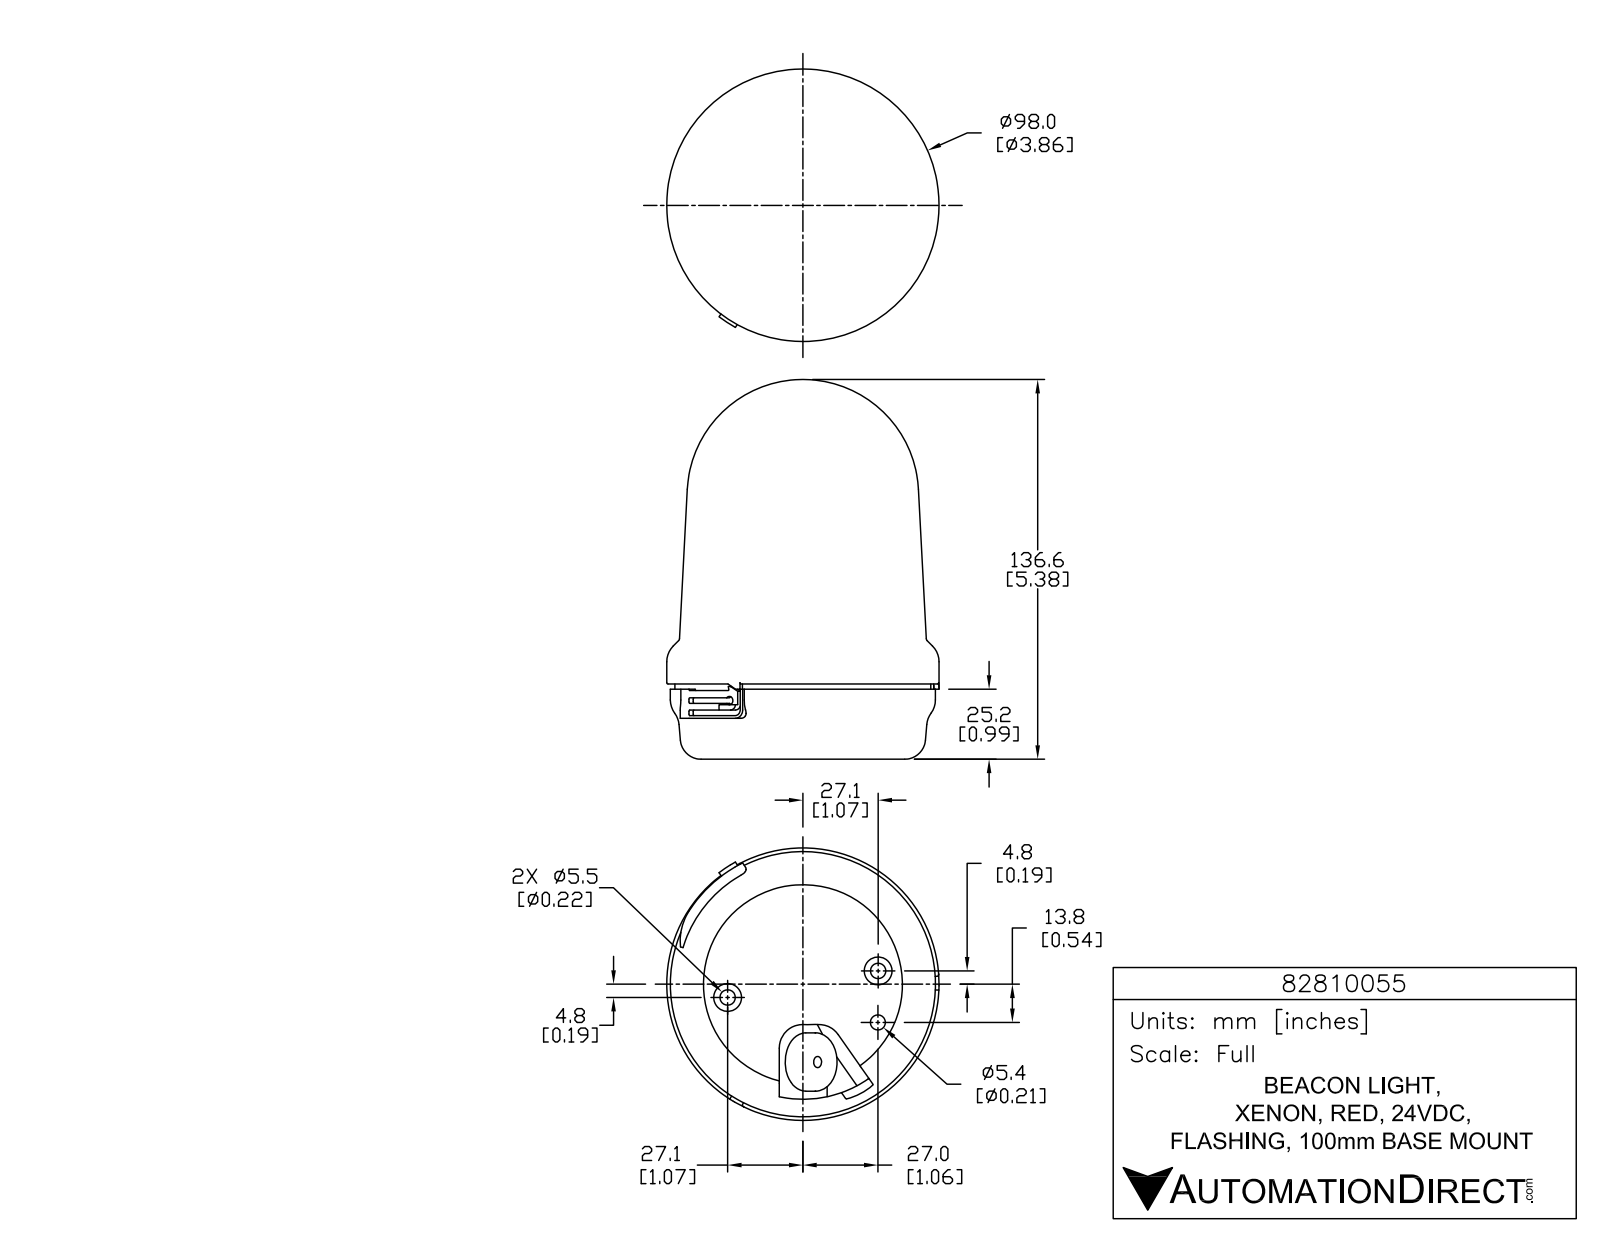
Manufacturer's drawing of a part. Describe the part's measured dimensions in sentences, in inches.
The part is named "82810055". Its 3-D file was written by "SolidWorks 2015 (AUTOMOTIVE_DESIGN)". It is 1 solid with 872 faces: 566 planar, 204 cylindrical and 102 other. Overall it measures 5.378 by 3.858 by 3.858 inches. Its volume is 44.69 cubic inches and its surface area 73.66 square inches. Round holes: 3 of diameter 0.059, 2 of diameter 0.217, 1 of diameter 0.157, 1 of diameter 0.213, 1 of diameter 2.819. Round bosses or shafts: 3 of diameter 0.339, 3 of diameter 0.084, 2 of diameter 0.394, 1 of diameter 3.858, 1 of diameter 3.756, 1 of diameter 3.626, 1 of diameter 0.827. Partial cylindrical surfaces (rounded edges, fillets, slot ends): 9 of radius 0.005, 6 of radius 0.005, 6 of radius 0.012, 6 of radius 0.012, 6 of radius 0.012, 6 of radius 0.196, 5 of radius 0.02, 4 of radius 0.039. The main face-to-face distances are 1.045, 0.972, 0.073, 0.02, 0.992, 1.065, 0.236, 0.579, 0.559, 0.413. The hole center spacings are 1.083, 0.73, 1.193, 2.158, 2.165.
